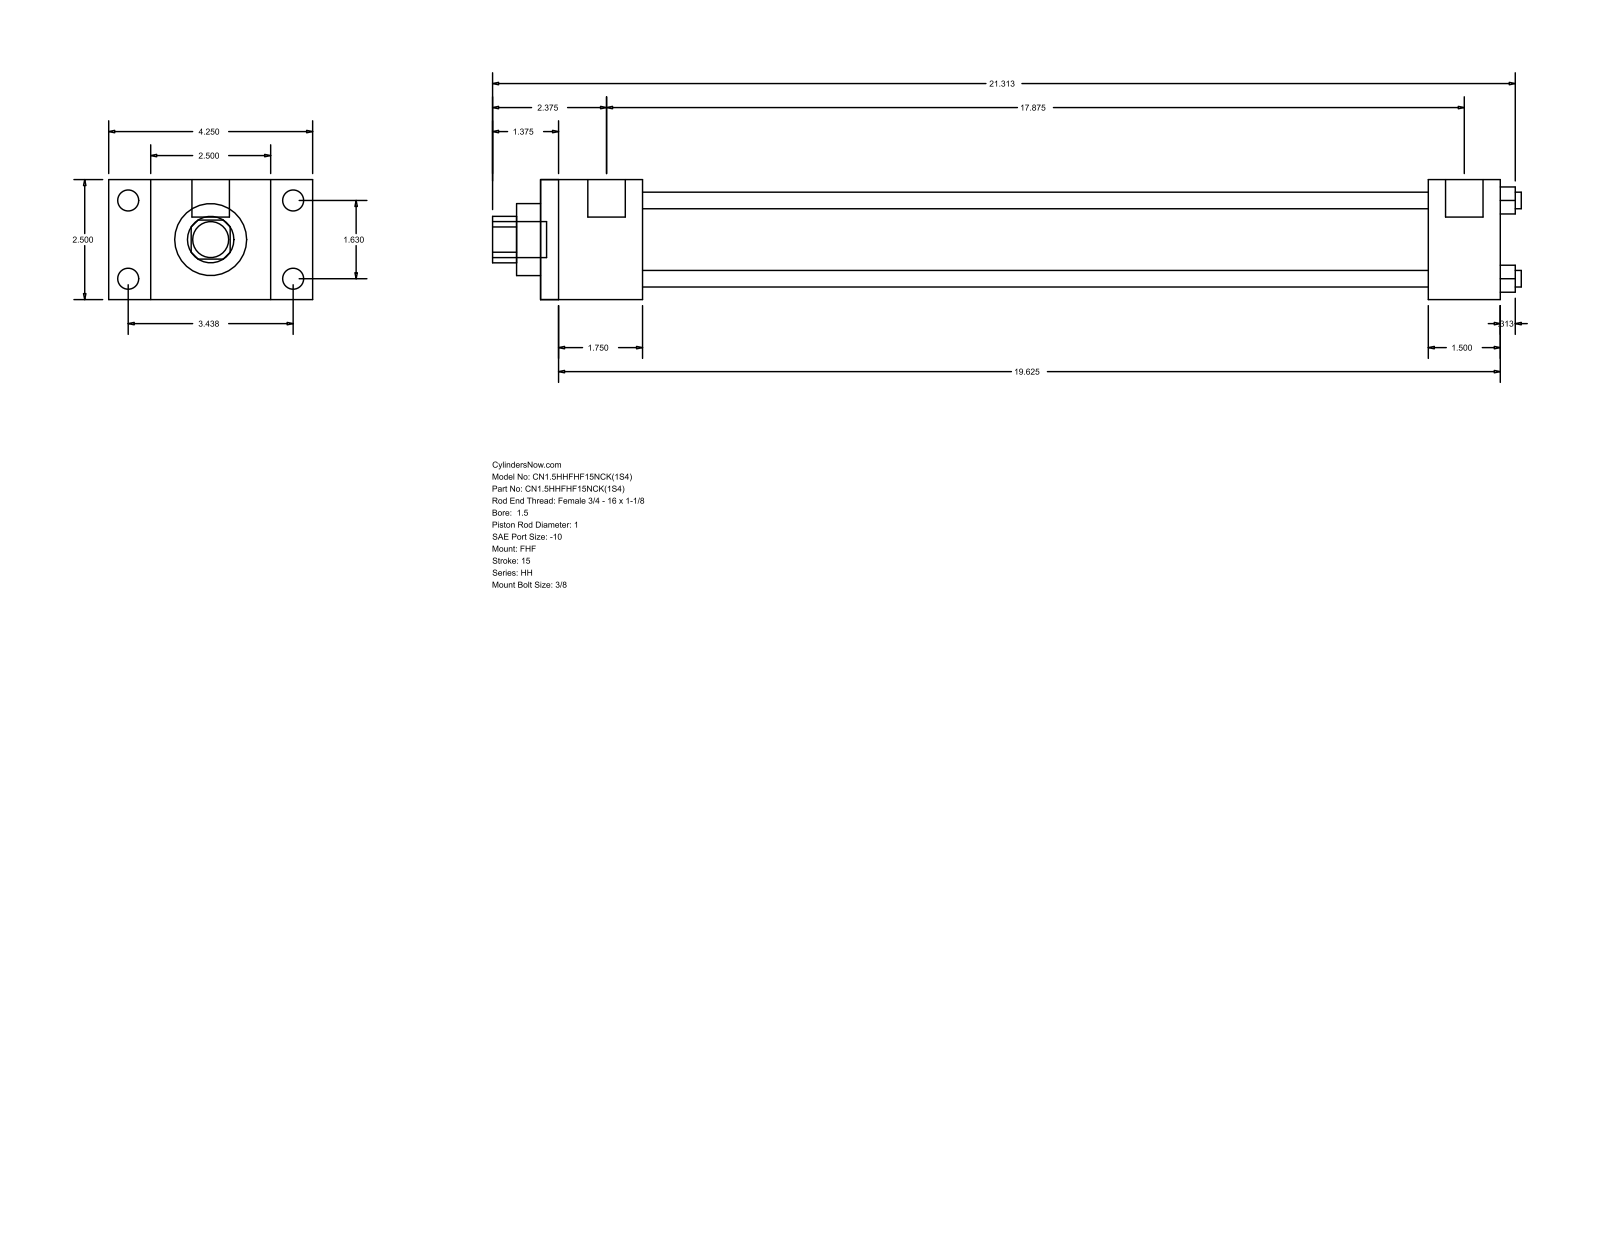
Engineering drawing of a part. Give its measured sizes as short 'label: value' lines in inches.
name: HH_FHF__0150_1
written by: GSSL Pune (CONFIG_CONTROL_DESIGN)
unit: in
bodies: 0 solids, 88 faces (60 planar, 28 cylindrical, 0 other)
size: 21.437 × 4.25 × 2.5
holes: 4× ⌀0.345, 1× ⌀1, 1× ⌀1.5, 1× ⌀1.75
bosses: 4× ⌀0.438, 4× ⌀0.219, 2× ⌀0.781, 1× ⌀0.75
rounds: 1× R0.484
face distances: 2.5, 0.875, 3.375, 2.125, 4.25, 20, 17.875, 18.5, 16.375, 1.5
hole spacings: 1.152, 1.63, 2.305
